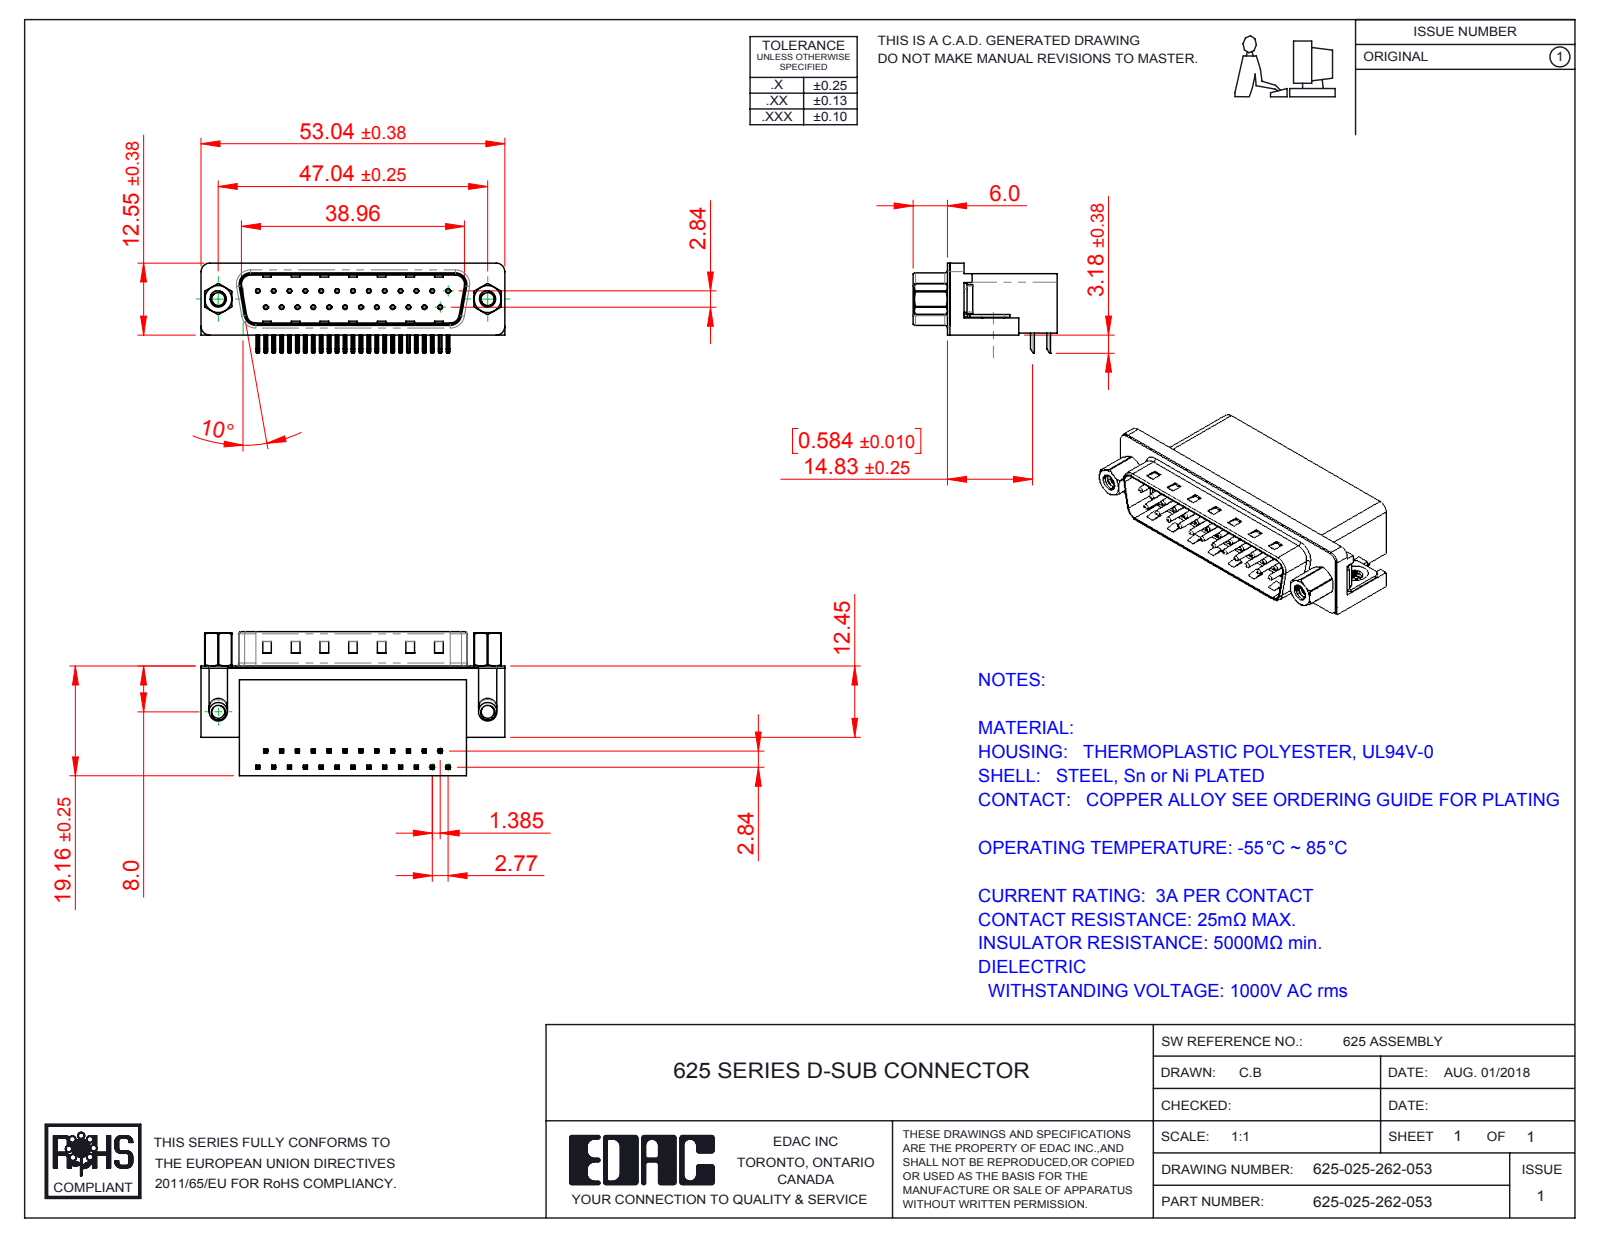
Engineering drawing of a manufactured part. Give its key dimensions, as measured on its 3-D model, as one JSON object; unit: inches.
{"part_name": "625 Shell_25 Socket; 625 Contact Top; 625 4-40 Threaded Board Mount; 625 Housing_25 Socket (+4 more)", "step_written_by": "SolidWorks 2016 (CONFIG_CONTROL_DESIGN)", "units": "inches", "bodies": {"solids": 33, "faces": 2423, "planar": 1429, "cylindrical": 745, "other": 249}, "overall_size": [2.088, 0.991, 0.619], "volume_in3": 0.573, "surface_area_in2": 14.61, "round_holes": [[0.014, 25], [0.031, 25], [0.089, 4], [0.09, 2], [0.157, 2], [0.189, 2], [0.197, 2]], "round_bosses_or_shafts": [[0.03, 25], [0.193, 2], [0.187, 2], [0.154, 2], [0.128, 2], [0.11, 2]], "partial_cylinders_radius": [[0.01, 108], [0.005, 50], [0.039, 16], [0.02, 9], [0.063, 8], [0.059, 7], [0.035, 4], [0.079, 4]], "face_to_face_distances": [0.016, 0.407, 0.739, 0.083, 0.345, 0.412, 0.428, 0.067, 0.754, 0.398], "hole_center_spacings": [0.124, 0.109, 0.436, 0.218, 0.327, 0.198, 0.545, 0.294]}
